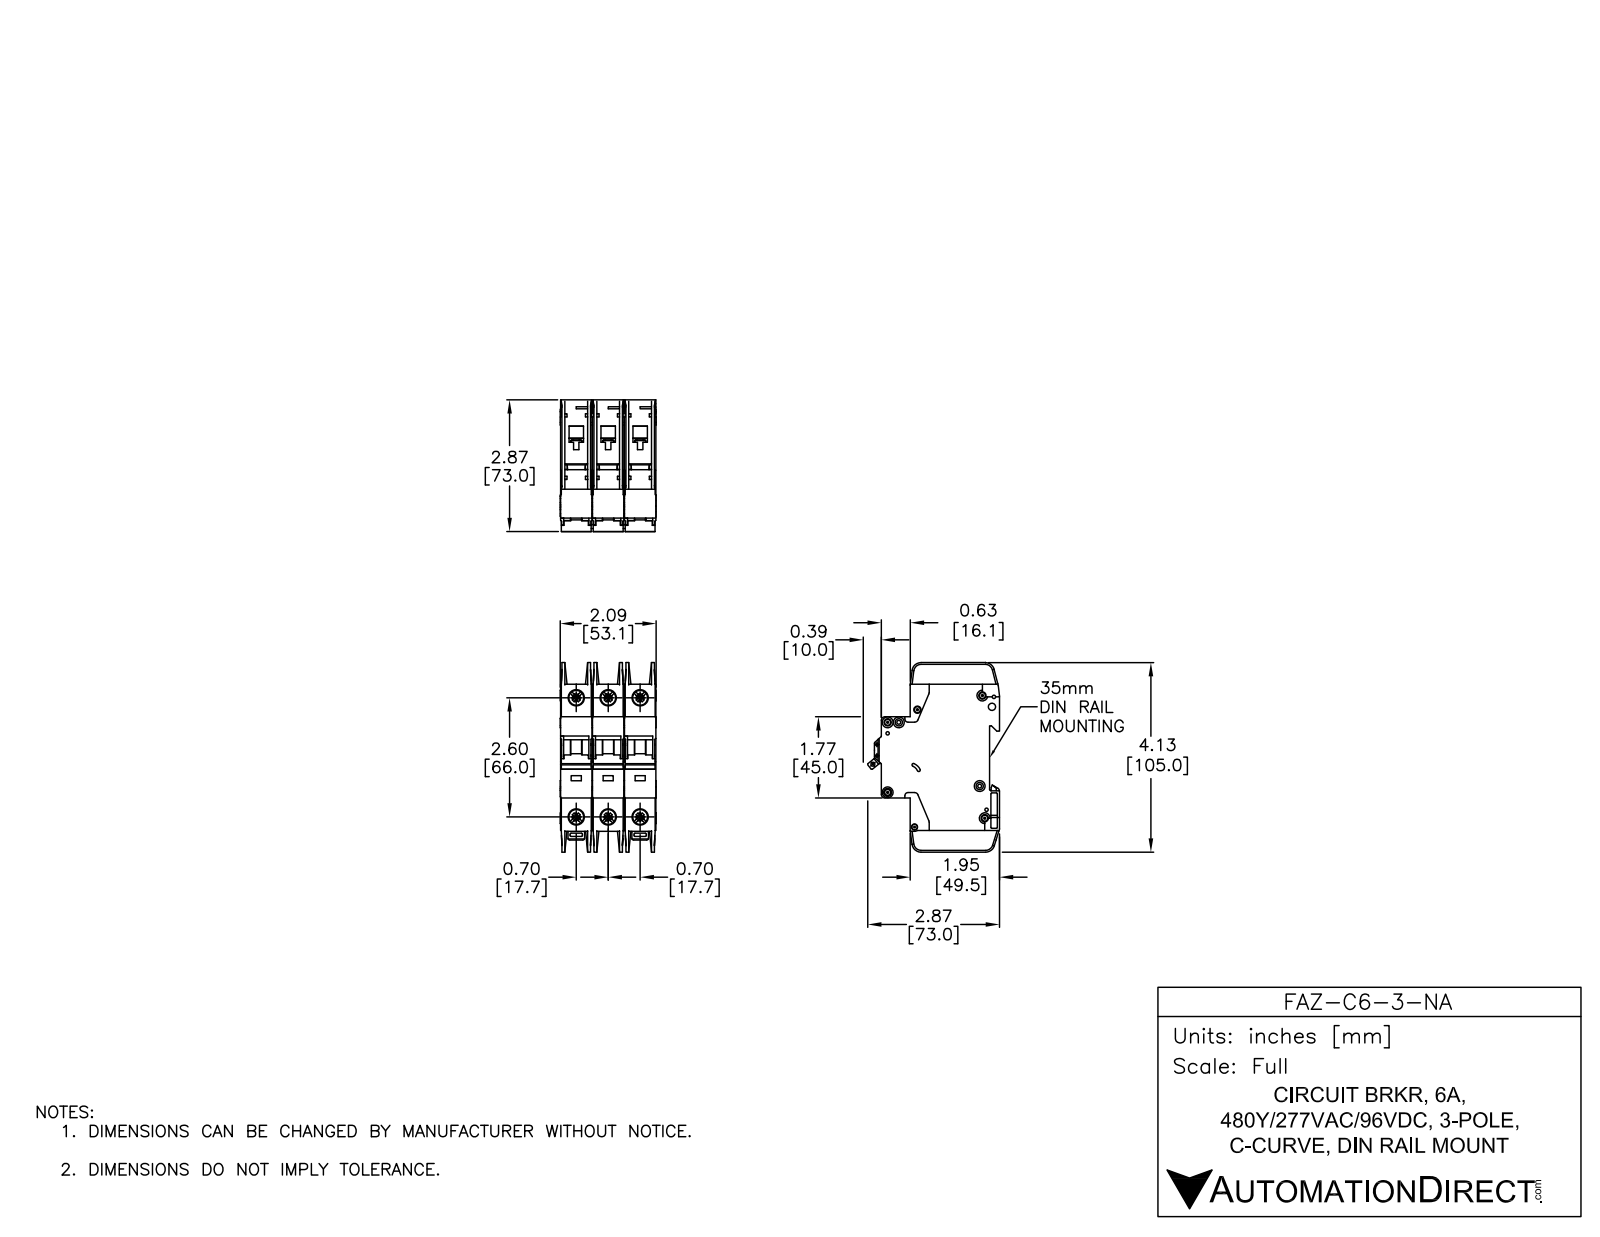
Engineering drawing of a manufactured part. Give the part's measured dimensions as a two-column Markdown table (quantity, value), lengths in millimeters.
| quantity | value |
| --- | --- |
| part name | FAZ-C6-3-NA |
| STEP written by | SolidWorks 2014 (AUTOMOTIVE_DESIGN) |
| units | millimeters |
| bodies | 9 solids, 2352 faces (1227 planar, 789 cylindrical, 336 other) |
| overall size | 105 × 73.04 × 53.1 |
| volume | 233 085 mm³ |
| surface area | 74 219 mm² |
| round holes (diameter × count) | 3.6 × 7, 7.15 × 6, 8.2 × 6, 1.09 × 2, 1.5 × 2, 4 × 2, 1.9 × 1, 2.15 × 1, 2.2 × 1, 2.55 × 1, 3.3 × 1, 3.4 × 1 |
| round bosses / shafts (diameter × count) | 6 × 7, 2.5 × 3 |
| partial cylindrical surfaces (radius × count) | 0.25 × 65, 0.5 × 30, 1 × 26, 2 × 14, 1.8 × 5, 5 × 5, 4 × 4, 0.2 × 2 |
| main face-to-face distances | 17.7, 35.4, 17.5, 35.2, 0.7, 15.05, 2.45, 1.75, 15.75, 13.3 |
| hole center spacings | 17.7, 68.33, 66, 6.2, 35.4, 74.89, 5.19, 6.1 |
